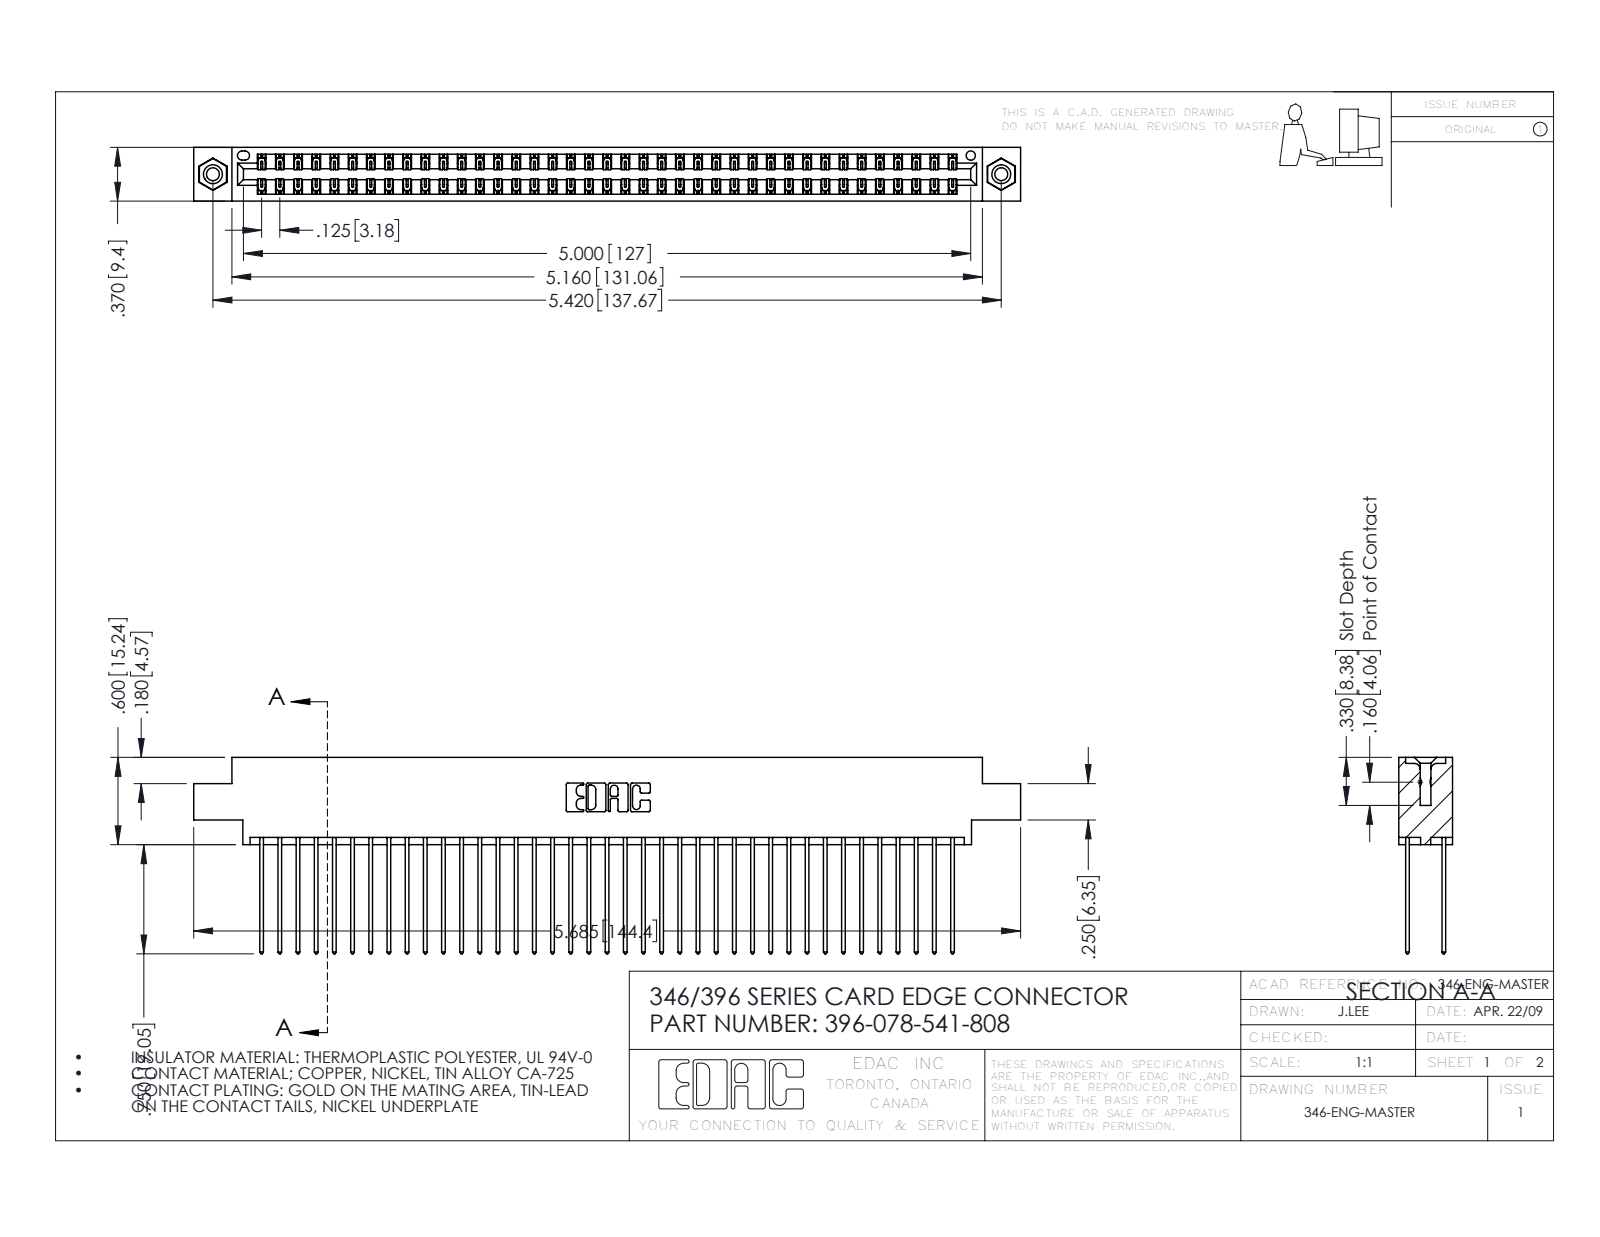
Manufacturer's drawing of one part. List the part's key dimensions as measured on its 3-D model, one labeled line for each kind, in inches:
Part name (STEP PRODUCT): 396-078-541-808; 345-250-001_345-250-003-102; 346 Part_0.170 Offset - 0.156 Dia-TI; 345-292-001_345-293-141
STEP written by: SolidWorks 2016 (CONFIG_CONTROL_DESIGN)
Units: inches
Bodies: 81 solids, 4242 faces (2842 planar, 1384 cylindrical, 16 other)
Overall size (bounding box): 5.685 × 1.35 × 0.37
Volume: 0.875 in³ · Surface area: 34.12 in²
Round holes (diameter × count): ⌀0.089 ×2, ⌀0.125 ×2, ⌀0.156 ×2, ⌀0.064 ×1
Round bosses / shafts (diameter × count): ⌀0.155 ×2
Partial cylindrical surfaces — rounded edges, fillets, slot ends (radius × count): R0.006 ×117, R0.01 ×78, R0.01 ×22, R0.007 ×6, R0.031 ×6, R0.026 ×3, R0.014 ×2, R0.022 ×2
Main face-to-face distances: 0.048, 0.322, 0.25, 0.072, 0.298, 0.025, 0.37, 0.275, 0.225, 0.222
Hole centre spacings: 0.246, 5.211, 5.42
